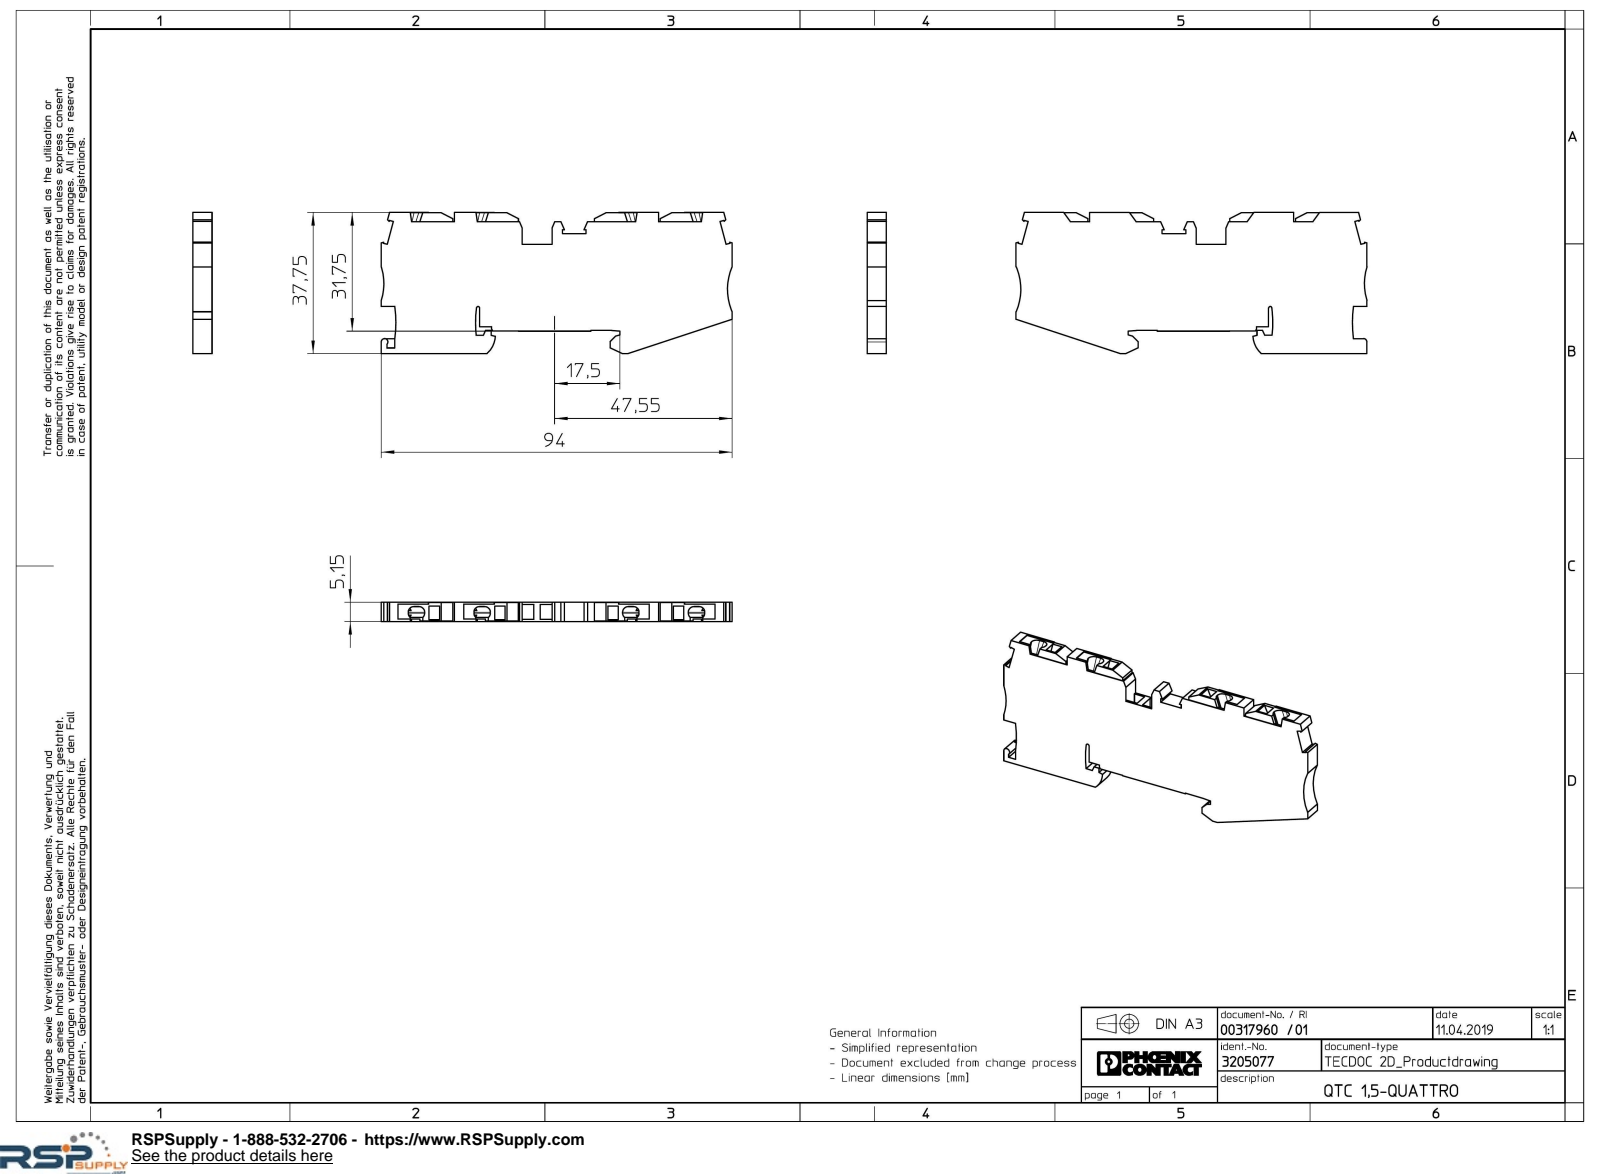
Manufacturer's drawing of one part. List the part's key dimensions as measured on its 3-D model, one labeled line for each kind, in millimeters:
Part name (STEP PRODUCT): QTC_1.5-QUATTRO-select
STEP written by: Creo Elements/Direct Modeling 20.1A 29-Sep-2018 (C) Parametric Technology GmbH (AUTOMOTIVE_DESIGN)
Units: millimetres
Bodies: 1 solid, 212 faces (188 planar, 24 cylindrical, 0 other)
Overall size (bounding box): 94 × 37.75 × 5.15
Volume: 14 222 mm³ · Surface area: 9 125 mm²
Partial cylindrical surfaces — rounded edges, fillets, slot ends (radius × count): R1.5 ×16, R0.4 ×2, R15 ×2, R31.69 ×2, R0.9 ×1, R6.6 ×1
Main face-to-face distances: 5.15, 4, 0.47, 31.65, 37.75, 0.5, 6, 1.21, 2.39, 5.05
